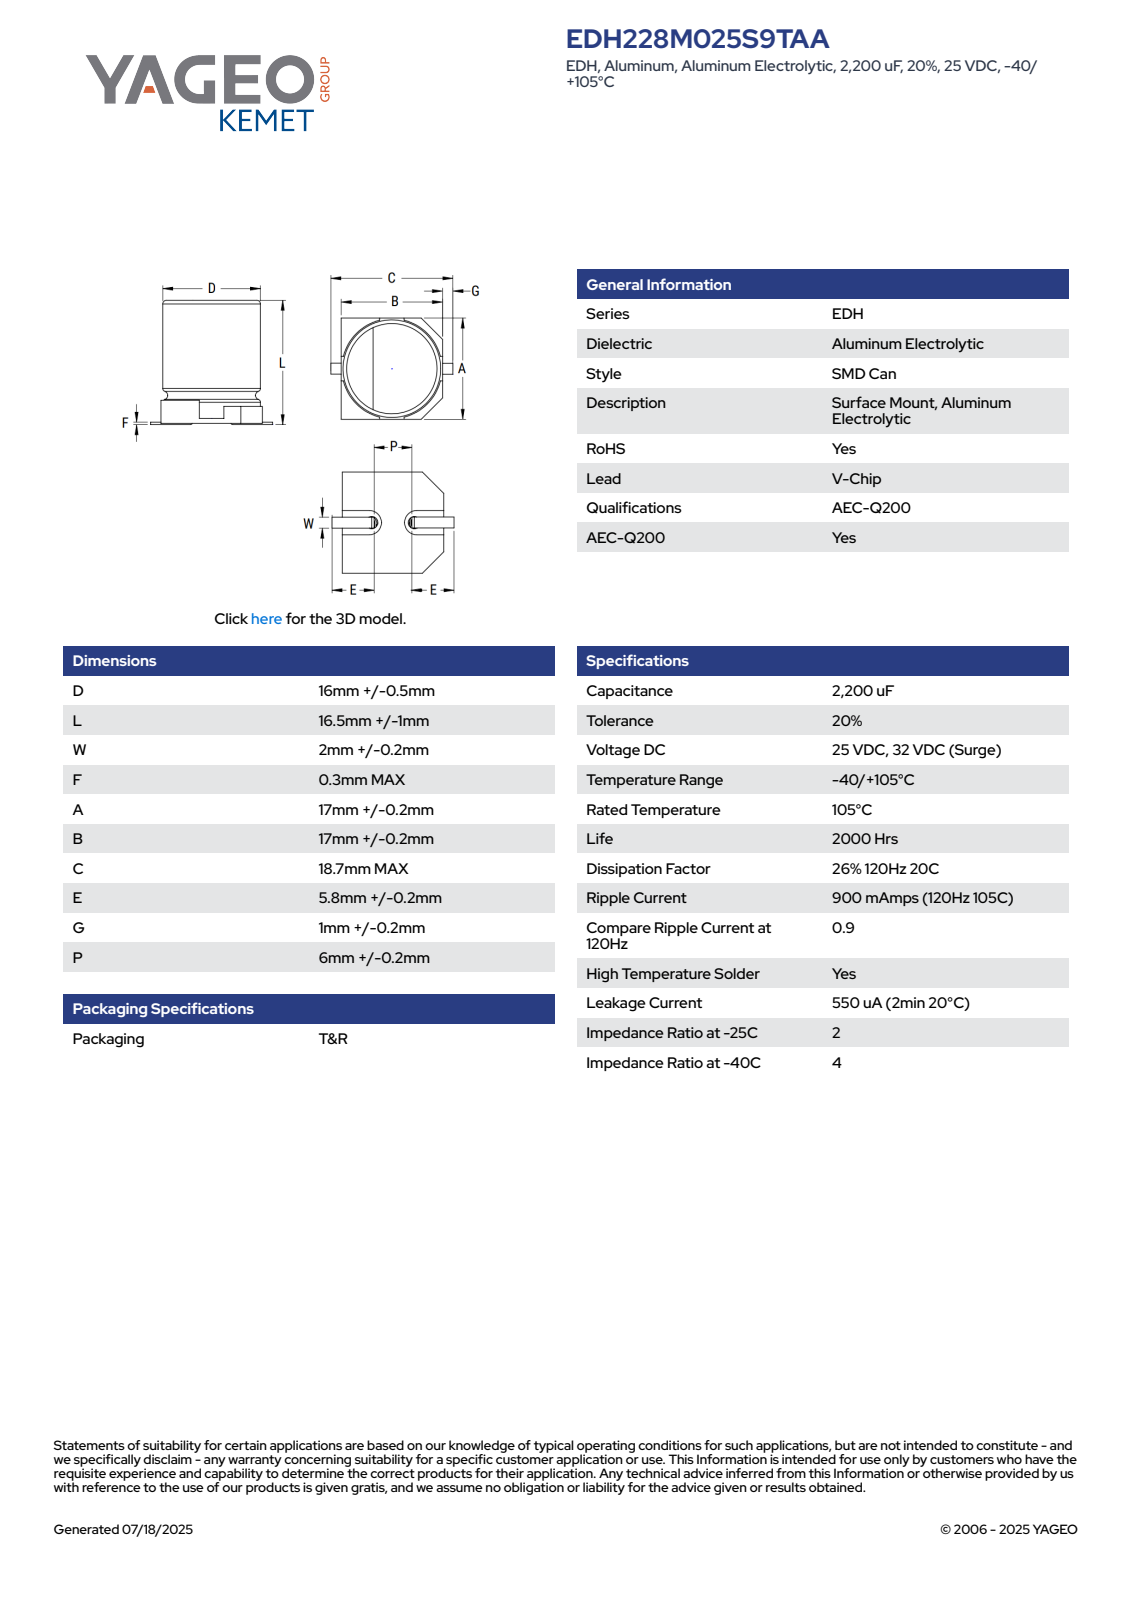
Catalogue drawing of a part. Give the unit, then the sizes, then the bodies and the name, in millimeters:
Units: millimetres
Overall size (bounding box): 18.2 × 17 × 16.5
Round bosses / shafts (diameter × count): ⌀15.77 ×1
Partial cylindrical surfaces — rounded edges, fillets, slot ends (radius × count): R0.2 ×2, R6.55 ×1, R8.25 ×1
Main face-to-face distances: 0.85, 16.7, 15.85, 16.71, 15.86, 16.5, 4.25, 3.4, 12.45, 12.46
Volume: 3 407 mm³ · Surface area: 2 016 mm²
Bodies: 5 solids, 78 faces (61 planar, 11 cylindrical, 6 other)
Part name (STEP PRODUCT): CAC_S_16X16.5_D16.5L17W2.2F0.3A16.5B16.5C18.7E6P6.2
STEP written by: SolidWorks 2014 (AUTOMOTIVE_DESIGN)
